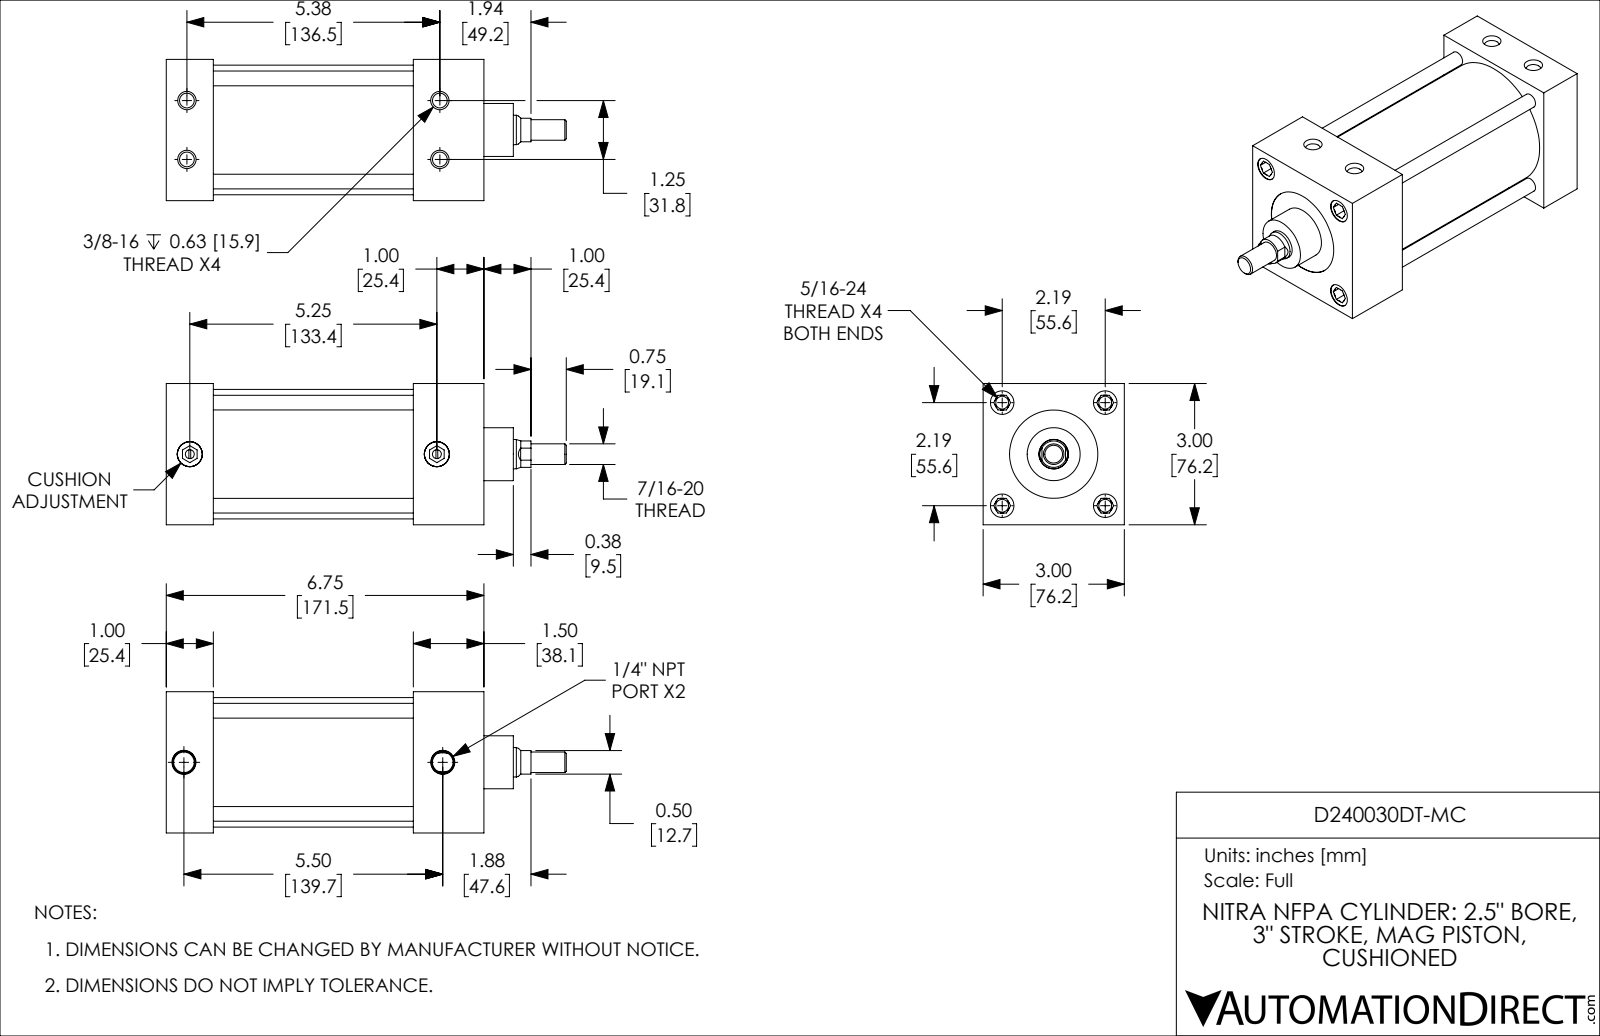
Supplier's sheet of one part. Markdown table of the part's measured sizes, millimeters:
| quantity | value |
| --- | --- |
| part name | D240030DT-MC_CUSHION; D240030DT-MC_BODY; D240030DT-MC_PISTON_KK1; D240030DT-MC |
| STEP written by | SolidWorks 2019 (CONFIG_CONTROL_DESIGN) |
| units | millimeters |
| bodies | 4 solids, 248 faces (90 planar, 78 cylindrical, 80 other) |
| overall size | 215.9 × 76.2 × 76.2 |
| volume | 572 400 mm³ |
| surface area | 129 900 mm² |
| round holes (diameter × count) | 6.9 × 4, 8 × 4, 12.7 × 4, 4.8 × 2, 11.1 × 2, 13.5 × 2, 15.9 × 1, 47.6 × 1, 63.5 × 1 |
| round bosses / shafts (diameter × count) | 7.9 × 4, 13.5 × 2, 69.9 × 1, 63.5 × 1, 28.6 × 1, 15.8 × 1, 11.1 × 1 |
| partial cylindrical surfaces (radius × count) | 7.1 × 1 |
| main face-to-face distances | 76.2, 25.4, 133.4, 108, 171.5, 146.1, 38.1, 31.8, 57.2, 114.3 |
| hole center spacings | 39.3, 55.6, 139, 16, 16, 31.8, 78.7, 136.5 |
